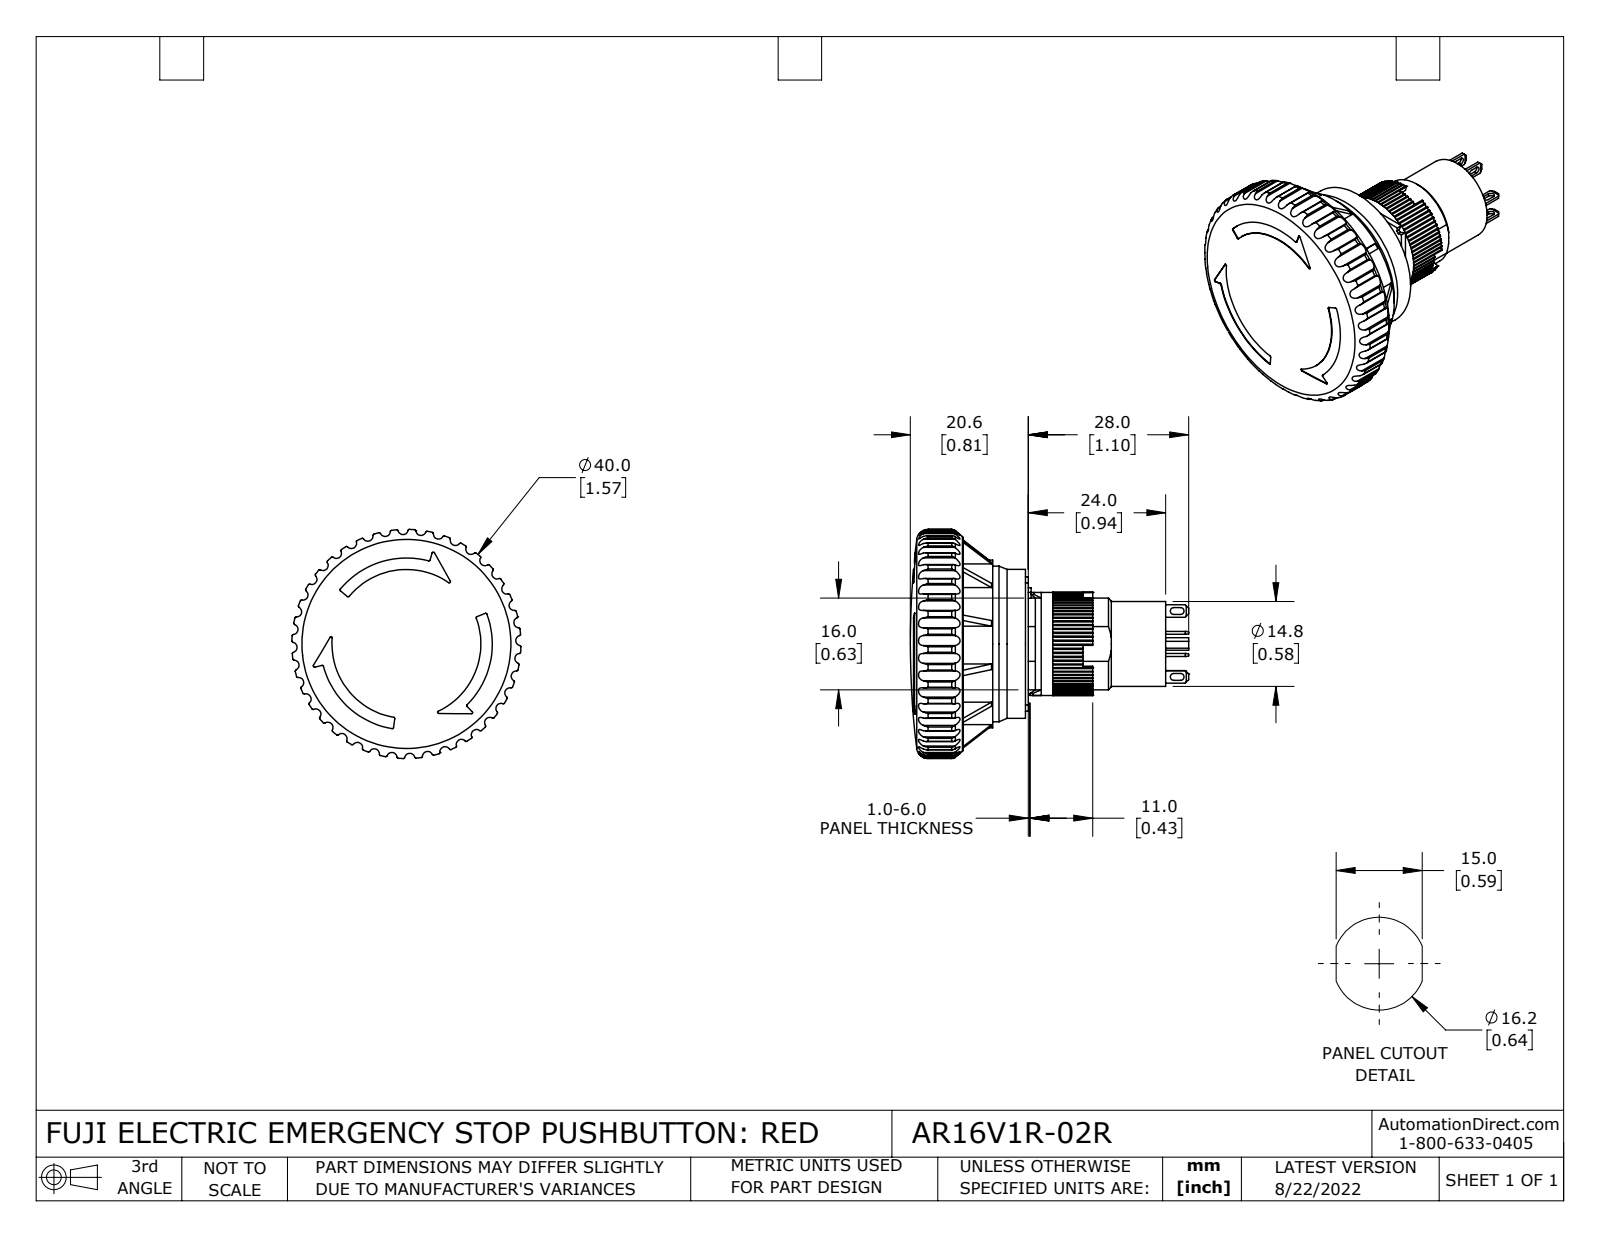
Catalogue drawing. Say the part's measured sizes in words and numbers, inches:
The part is named "AR16V1R-02R". Its 3-D file was written by "SolidWorks 2021 (CONFIG_CONTROL_DESIGN)". It is 5 solids with 1001 faces: 495 planar, 410 cylindrical and 96 other. Overall it measures 1.913 by 1.575 by 1.575 inches. Its volume is 0.963 cubic inches and its surface area 19.04 square inches. Round holes: 1 of diameter 0.583, 1 of diameter 0.63, 1 of diameter 0.709, 1 of diameter 1.069, 1 of diameter 1.433. Round bosses or shafts: 1 of diameter 1.154, 1 of diameter 1.024, 1 of diameter 0.858, 1 of diameter 0.236. Partial cylindrical surfaces (rounded edges, fillets, slot ends): 80 of radius 0.008, 80 of radius 0.01, 40 of radius 0.035, 8 of radius 0.02, 8 of radius 0.024, 2 of radius 0.039, 1 of radius 0.031, 1 of radius 0.114. The main face-to-face distances are 0.039, 0.421, 0.53, 0.108, 0.02, 0.069, 0.856, 0.49, 0.089, 0.049.
